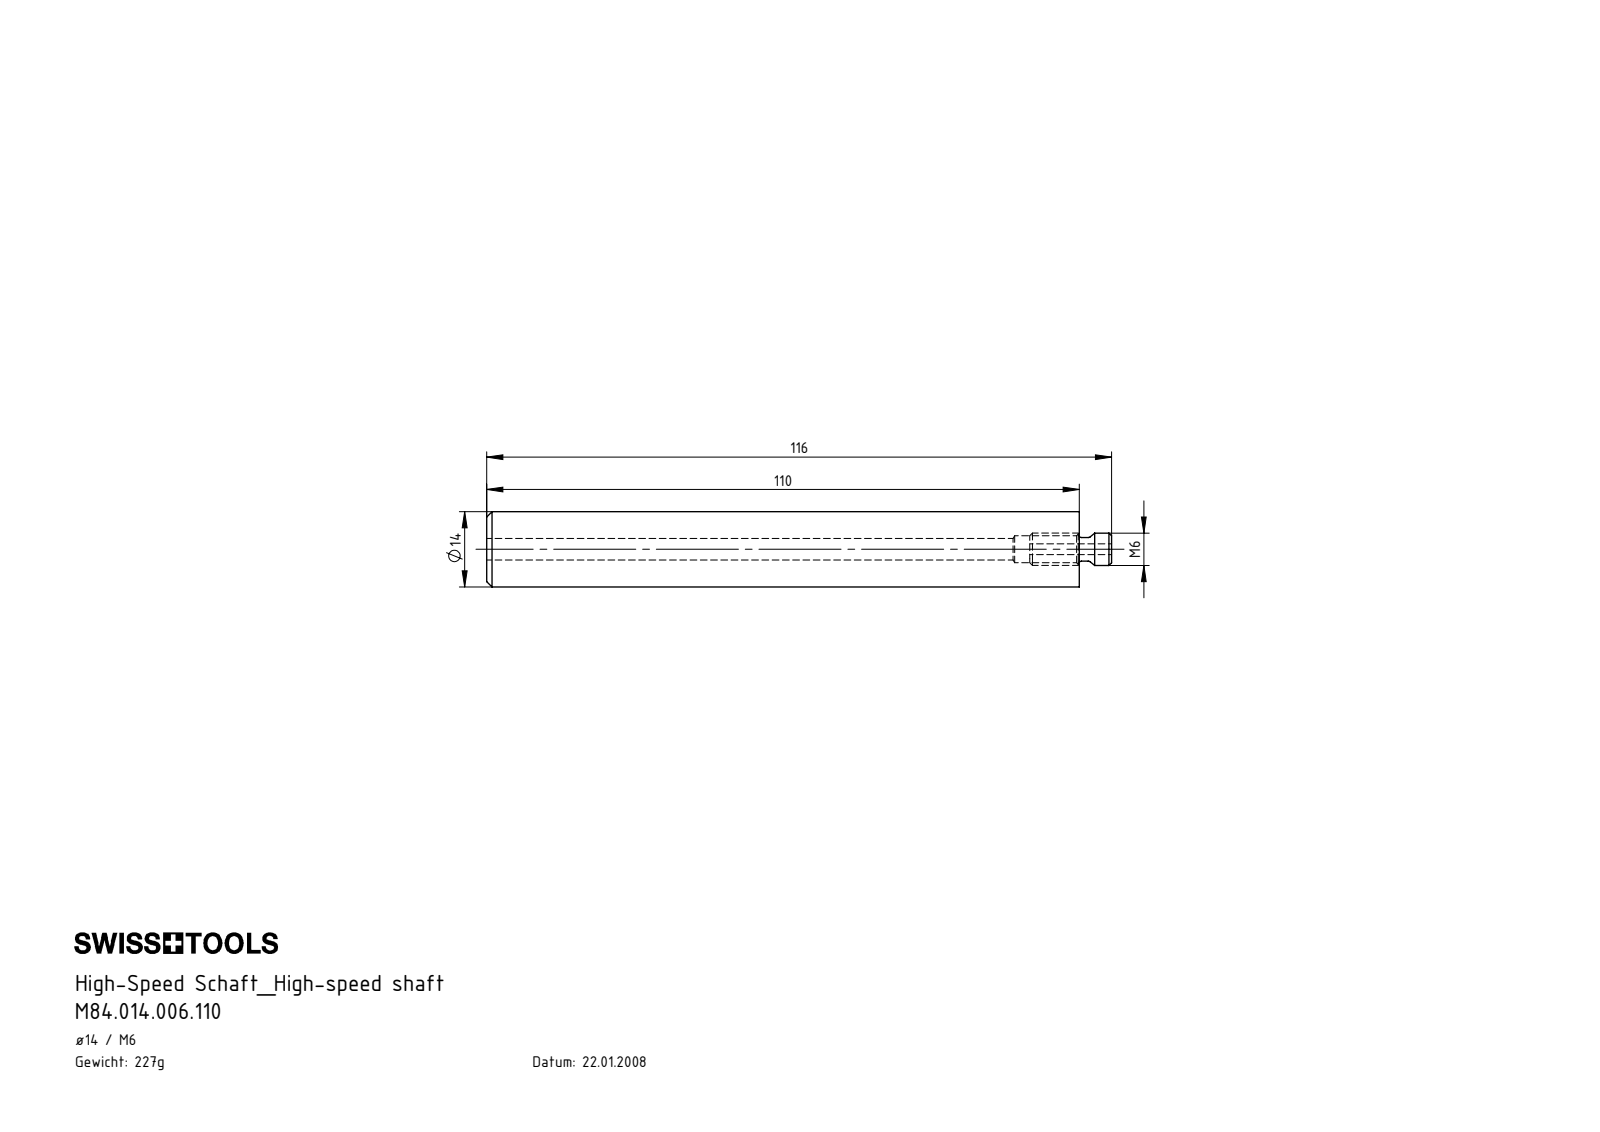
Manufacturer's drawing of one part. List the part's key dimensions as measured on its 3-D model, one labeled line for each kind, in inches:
Part name (STEP PRODUCT): HM1-BG1.006.015_A; U14.HS6.K01.110; HM1-U14.001.110_A
STEP written by: SolidWorks 2017 (AUTOMOTIVE_DESIGN)
Units: inches
Bodies: 2 solids, 20 faces (5 planar, 7 cylindrical, 8 other)
Overall size (bounding box): 4.567 × 0.551 × 0.551
Volume: 0.963 in³ · Surface area: 10.74 in²
Round holes (diameter × count): ⌀0.079 ×1, ⌀0.157 ×1, ⌀0.197 ×1
Round bosses / shafts (diameter × count): ⌀0.551 ×1, ⌀0.236 ×1, ⌀0.173 ×1
Main face-to-face distances: 4.331, 3.969, 0.362, 4.567, 0.598, 0.236, 4.323, 0.354, 0.244
